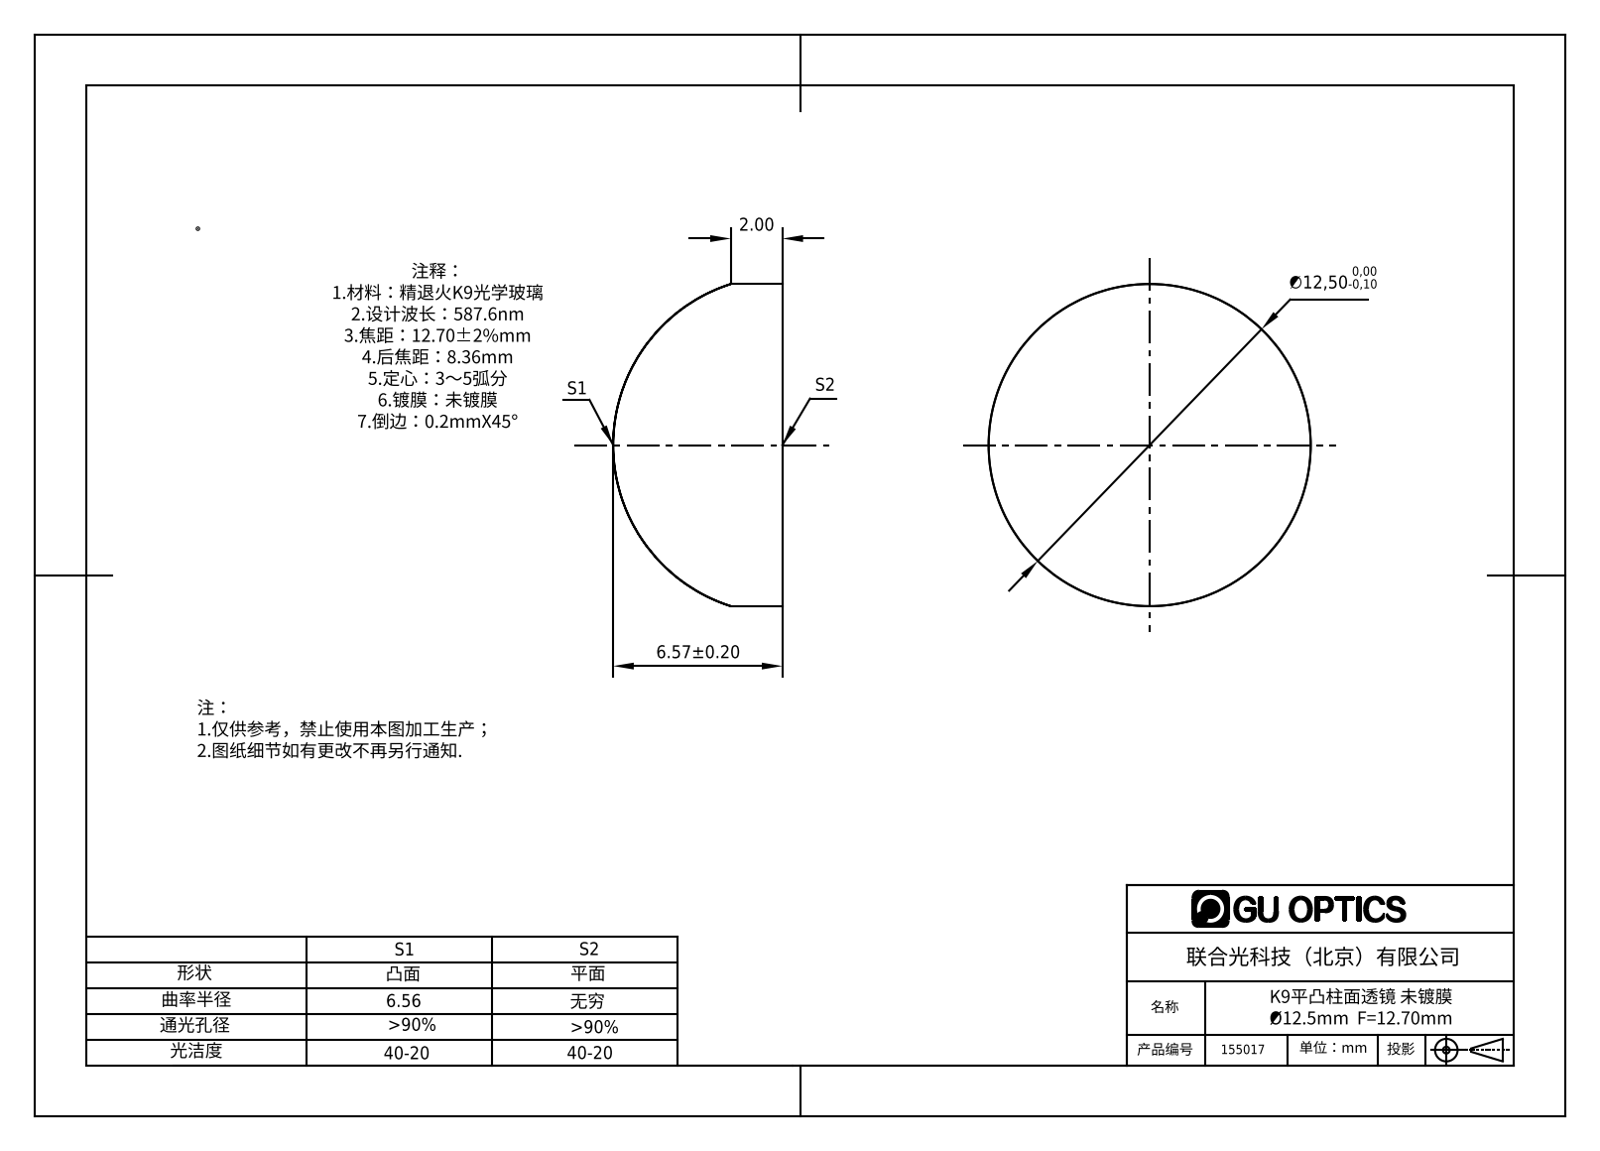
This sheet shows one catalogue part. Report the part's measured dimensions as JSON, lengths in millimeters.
{"part_name": "155017", "step_written_by": "SolidWorks 2016 (AUTOMOTIVE_DESIGN)", "units": "millimeters", "bodies": {"solids": 1, "faces": 4, "planar": 1, "cylindrical": 3, "other": 0}, "overall_size": [12.5, 12.5, 6.57], "volume_mm3": 699, "surface_area_mm2": 451, "round_bosses_or_shafts": [[12.5, 1]], "partial_cylinders_radius": [[6.56, 1]]}
